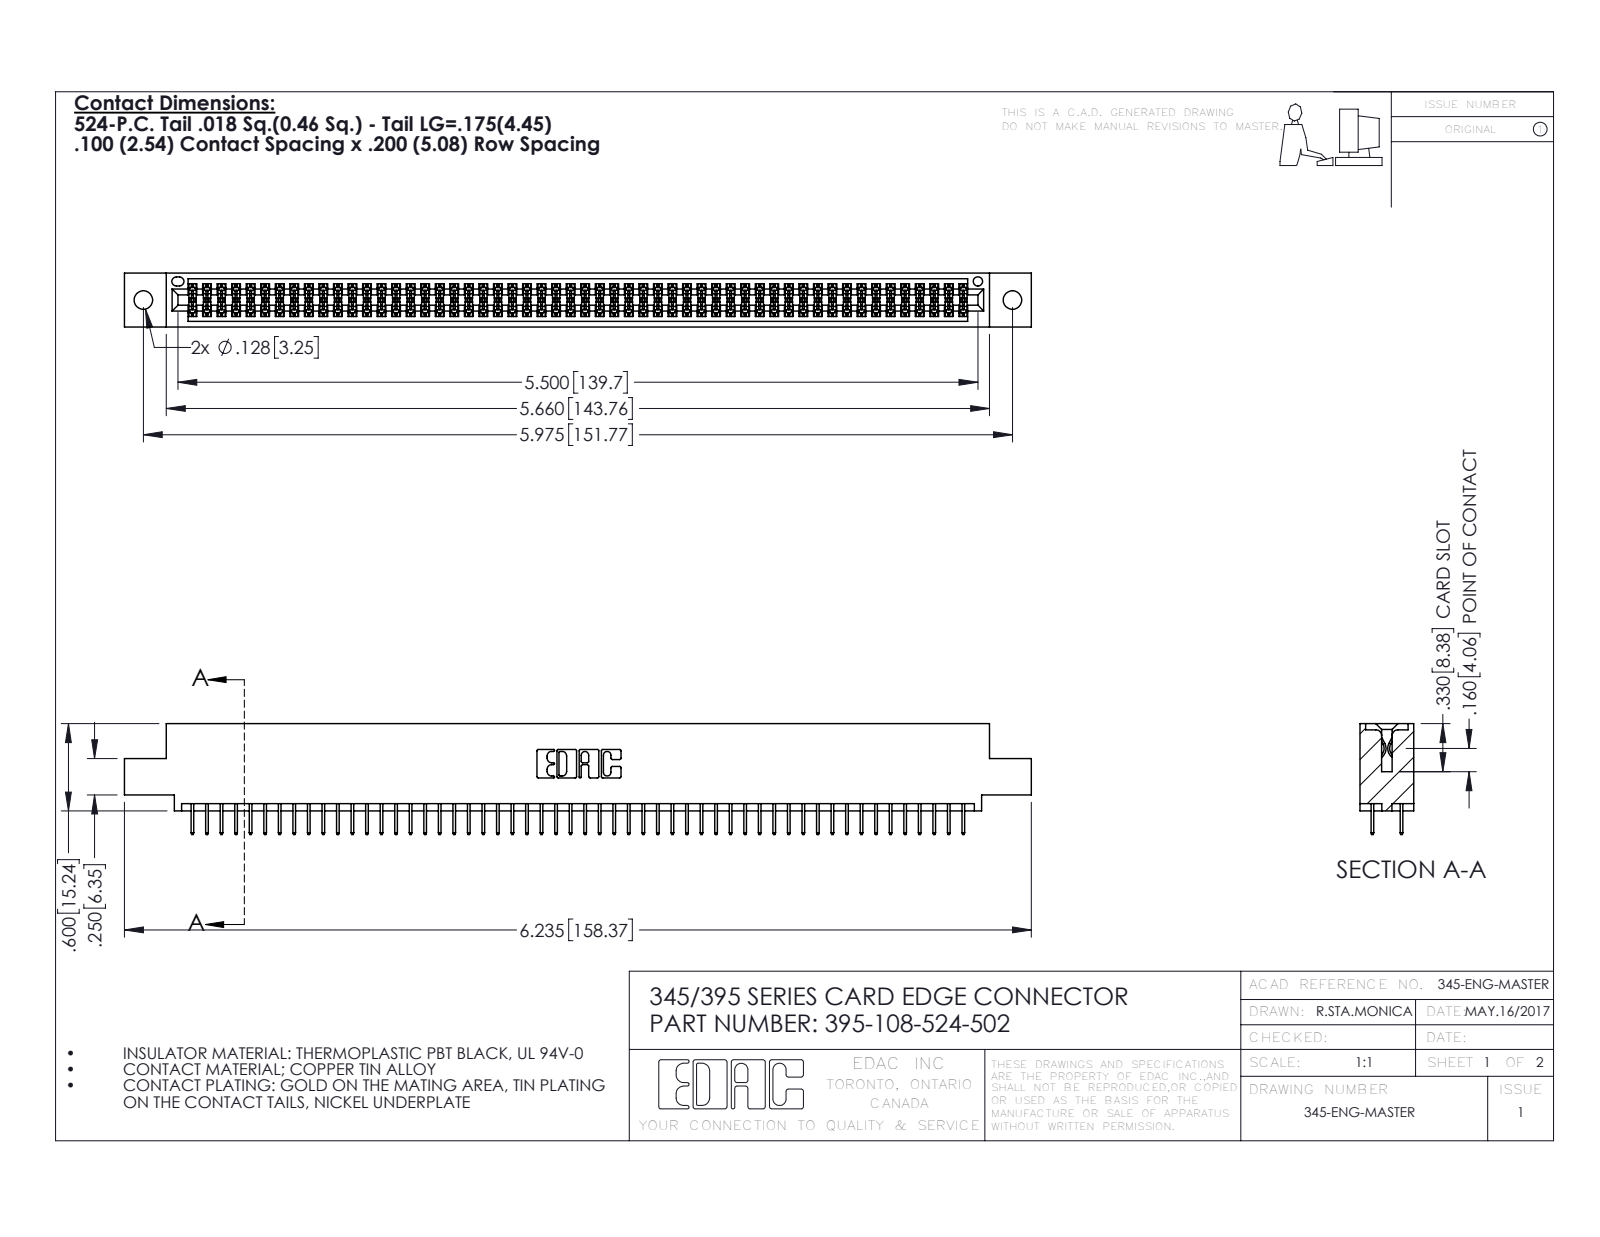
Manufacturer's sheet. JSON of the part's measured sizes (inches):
{"part_name": "345 Part_0.110 Offset - 0.128 Dia; 395-108-524-502; 345-292-001_345-293-124", "step_written_by": "SolidWorks 2016 (CONFIG_CONTROL_DESIGN)", "units": "inches", "bodies": {"solids": 109, "faces": 5962, "planar": 4296, "cylindrical": 1666, "other": 0}, "overall_size": [6.235, 0.762, 0.37], "volume_in3": 0.929, "surface_area_in2": 34.29, "round_holes": [[0.128, 2], [0.064, 1]], "partial_cylinders_radius": [[0.006, 162], [0.01, 22], [0.007, 6], [0.031, 6], [0.026, 3], [0.014, 2], [0.019, 2], [0.022, 2]], "face_to_face_distances": [0.072, 0.298, 0.2, 0.37, 0.098, 0.272, 0.025, 0.225, 0.072, 0.175], "hole_center_spacings": [0.27, 5.739, 5.975]}
